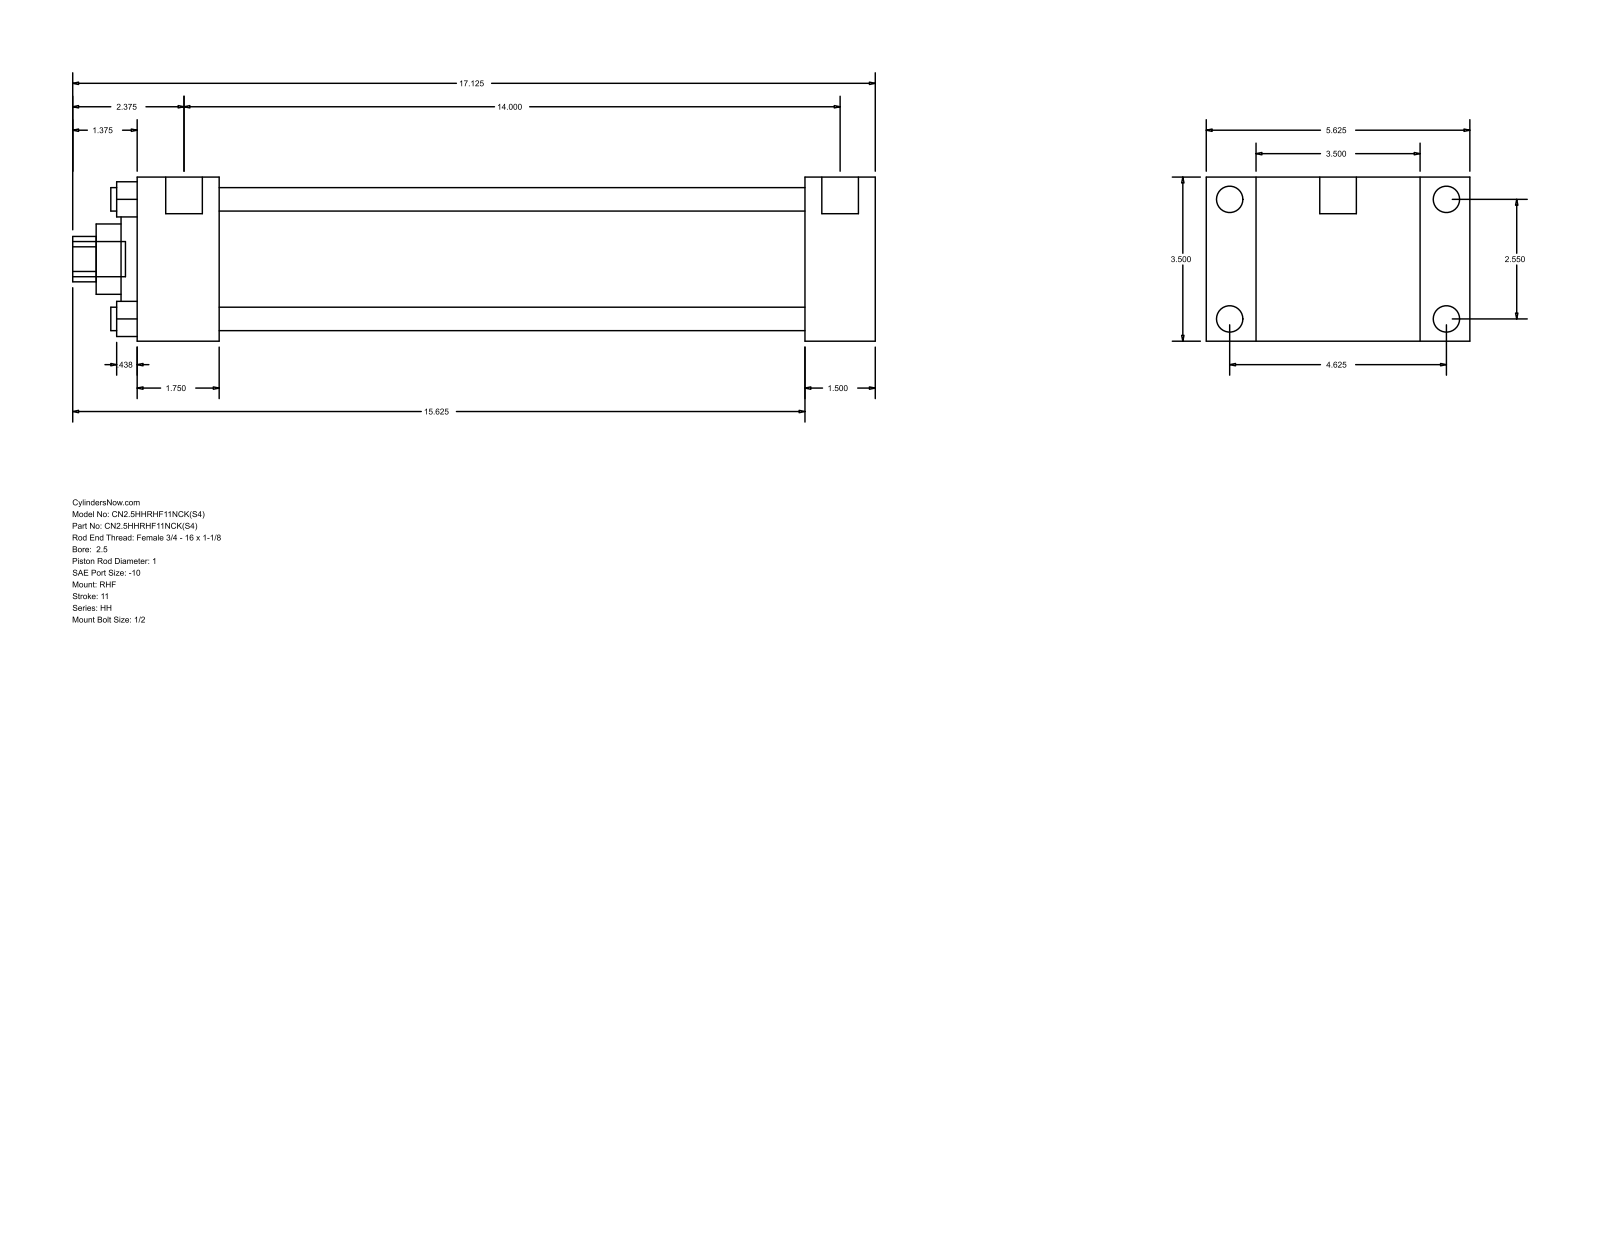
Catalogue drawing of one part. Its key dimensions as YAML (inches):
part_name: "HH_RHF__0250_1"
step_written_by: "GSSL Pune (CONFIG_CONTROL_DESIGN)"
units: inches
bodies: {solids: 0, faces: 90, planar: 61, cylindrical: 29, other: 0}
overall_size: [17.125, 5.625, 3.5]
round_holes:
  - {diameter: 0.5, count: 4}
  - {diameter: 1, count: 1}
  - {diameter: 1.5, count: 1}
  - {diameter: 2.375, count: 1}
  - {diameter: 2.875, count: 1}
round_bosses_or_shafts:
  - {diameter: 0.563, count: 4}
  - {diameter: 0.219, count: 4}
  - {diameter: 0.781, count: 2}
  - {diameter: 0.75, count: 1}
partial_cylinders:
  - {radius: 0.484, count: 1}
face_to_face_distances: [3.5, 1.5, 1.063, 4.563, 14.25, 15.75, 5.625, 1.75, 12.5, 14]
hole_center_spacings: [1.803, 2.55, 3.606]
